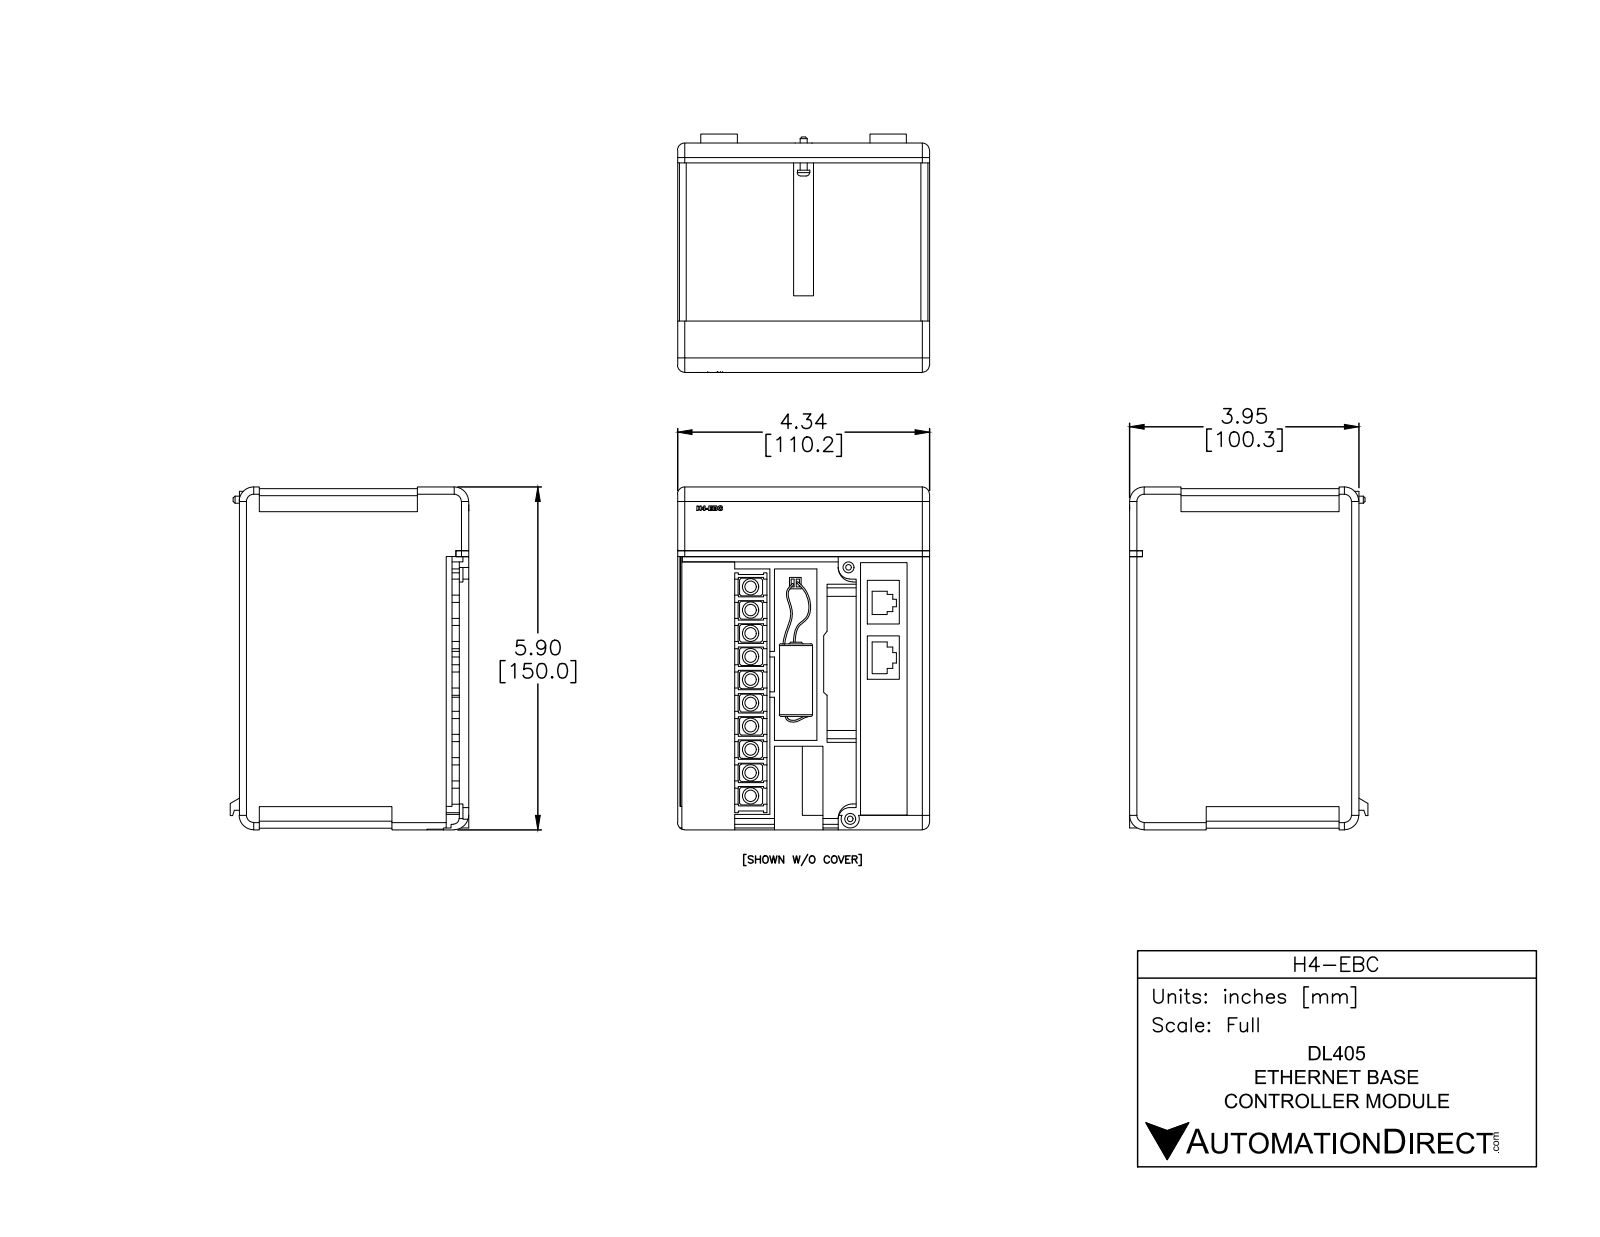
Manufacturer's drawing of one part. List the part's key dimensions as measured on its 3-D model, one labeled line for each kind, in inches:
Part name (STEP PRODUCT): H4-EBC
STEP written by: SolidWorks 2014 (AUTOMOTIVE_DESIGN)
Units: inches
Bodies: 3 solids, 688 faces (557 planar, 76 cylindrical, 55 other)
Overall size (bounding box): 5.905 × 4.34 × 4.106
Volume: 90.7 in³ · Surface area: 171.9 in²
Round holes (diameter × count): ⌀0.1 ×2, ⌀0.12 ×2, ⌀0.188 ×1, ⌀0.188 ×1
Round bosses / shafts (diameter × count): ⌀0.279 ×10, ⌀0.567 ×1, ⌀0.212 ×1, ⌀0.123 ×1
Partial cylindrical surfaces — rounded edges, fillets, slot ends (radius × count): R0.125 ×8, R0.25 ×6, R0.12 ×4, R0.2 ×2, R0.1 ×1, R0.145 ×1, R0.156 ×1, R0.171 ×1
Main face-to-face distances: 4.34, 0.03, 5.845, 5.875, 3.95, 0.715, 0.115, 3.235, 0.67, 0.08
Hole centre spacings: 0.69, 1.248, 1.681, 2.824, 4.054, 4.329
